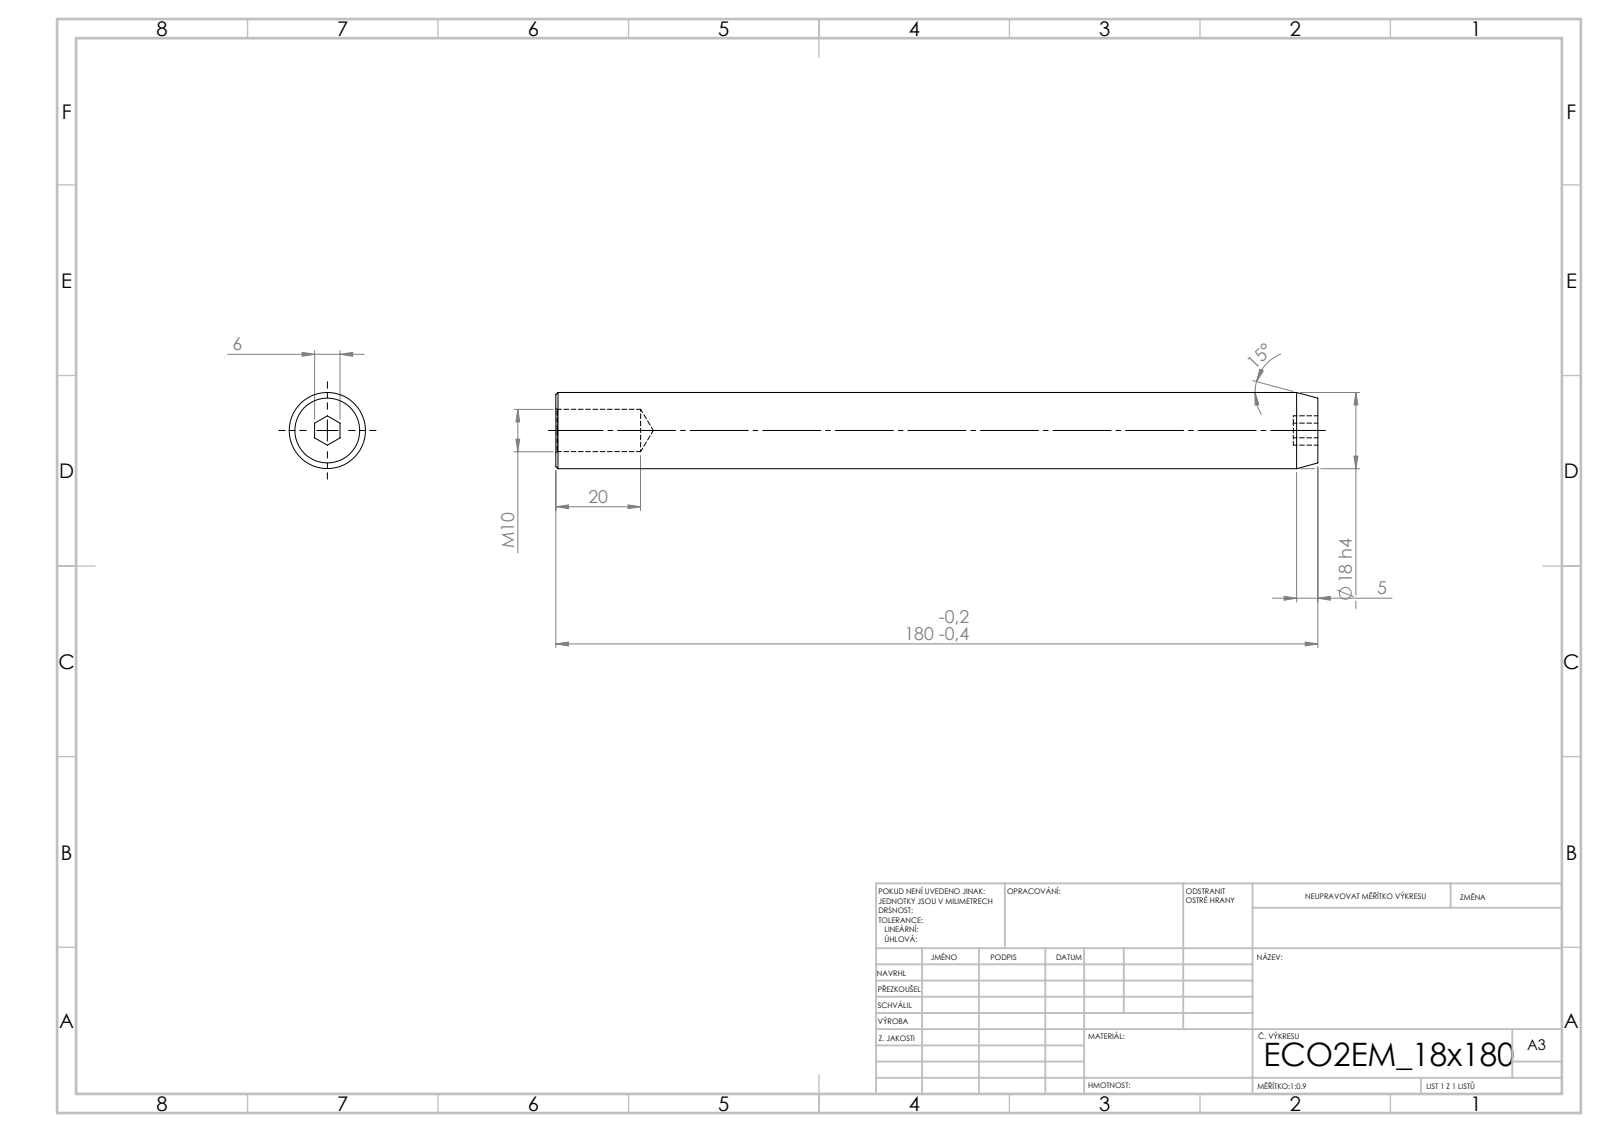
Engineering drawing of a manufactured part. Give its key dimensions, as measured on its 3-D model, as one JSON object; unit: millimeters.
{"step_written_by": "SolidWorks 2019 (CONFIG_CONTROL_DESIGN)", "units": "millimeters", "bodies": {"solids": 1, "faces": 21, "planar": 9, "cylindrical": 4, "other": 8}, "overall_size": [180, 18, 18], "volume_mm3": 43787, "surface_area_mm2": 11347, "round_holes": [[10, 1]], "round_bosses_or_shafts": [[18, 1]], "face_to_face_distances": [180, 6, 5.8, 174.2]}
